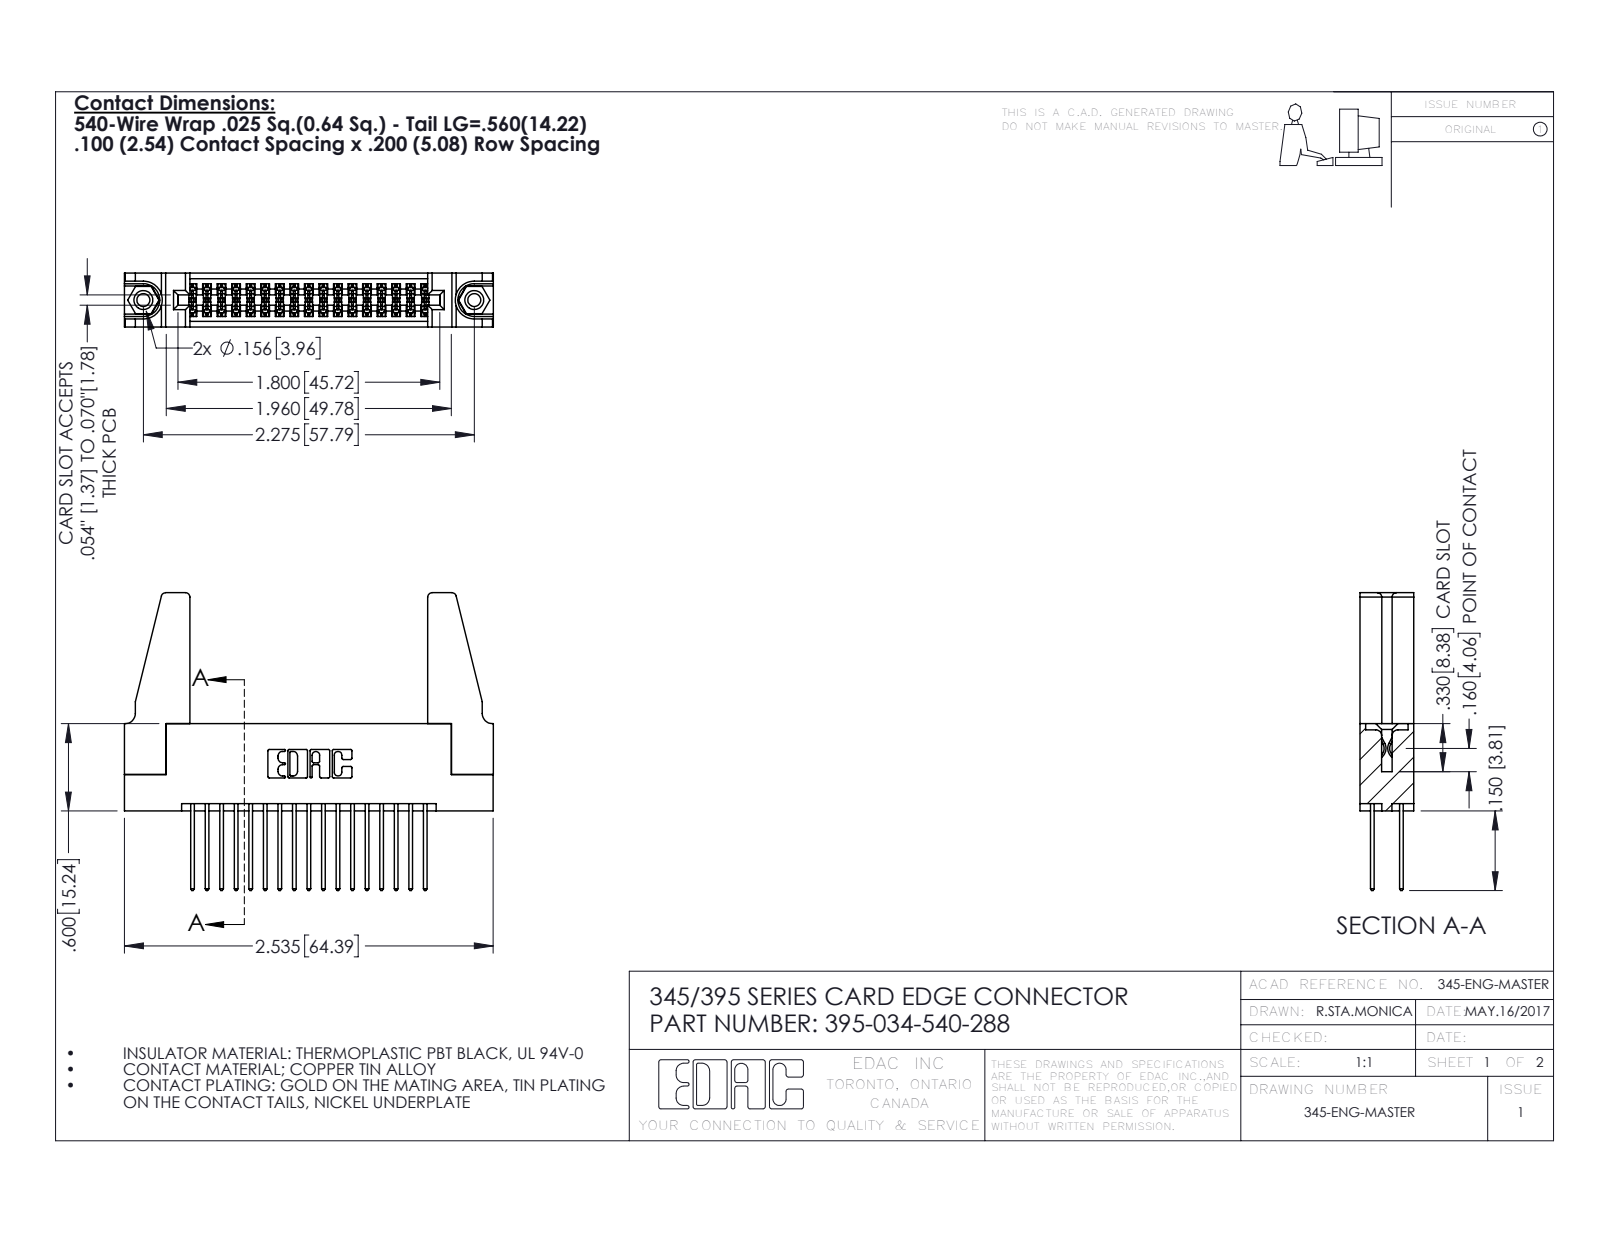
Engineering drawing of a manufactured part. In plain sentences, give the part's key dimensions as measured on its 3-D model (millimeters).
The part is named "345-220-078_345-220-088; 345 Part_Flush Mounting Lugs - 0.156 Dia-TH; 345-250-001_345-250-001-102; 345-292-001_345-293-140 (+1 more)". Its 3-D file was written by "SolidWorks 2016 (CONFIG_CONTROL_DESIGN)". It is 39 solids with 1950 faces: 1274 planar, 660 cylindrical and 16 other. Overall it measures 64.4 by 52 by 9.4 millimeters. Its volume is 9 410 cubic millimeters and its surface area 12 340 square millimeters. Round holes: 2 of diameter 2.3, 2 of diameter 3.2, 2 of diameter 4, 1 of diameter 1.6. Round bosses or shafts: 2 of diameter 3.9. Partial cylindrical surfaces (rounded edges, fillets, slot ends): 51 of radius 0.2, 34 of radius 0.3, 22 of radius 0.3, 8 of radius 0.8, 6 of radius 0.2, 6 of radius 0.8, 3 of radius 0.7, 2 of radius 0.4. The main face-to-face distances are 1.8, 7.6, 9.4, 5.1, 2.5, 6.9, 0.6, 5.7, 4.4, 3.8. The hole center spacings are 6.9, 51.8, 57.8.
